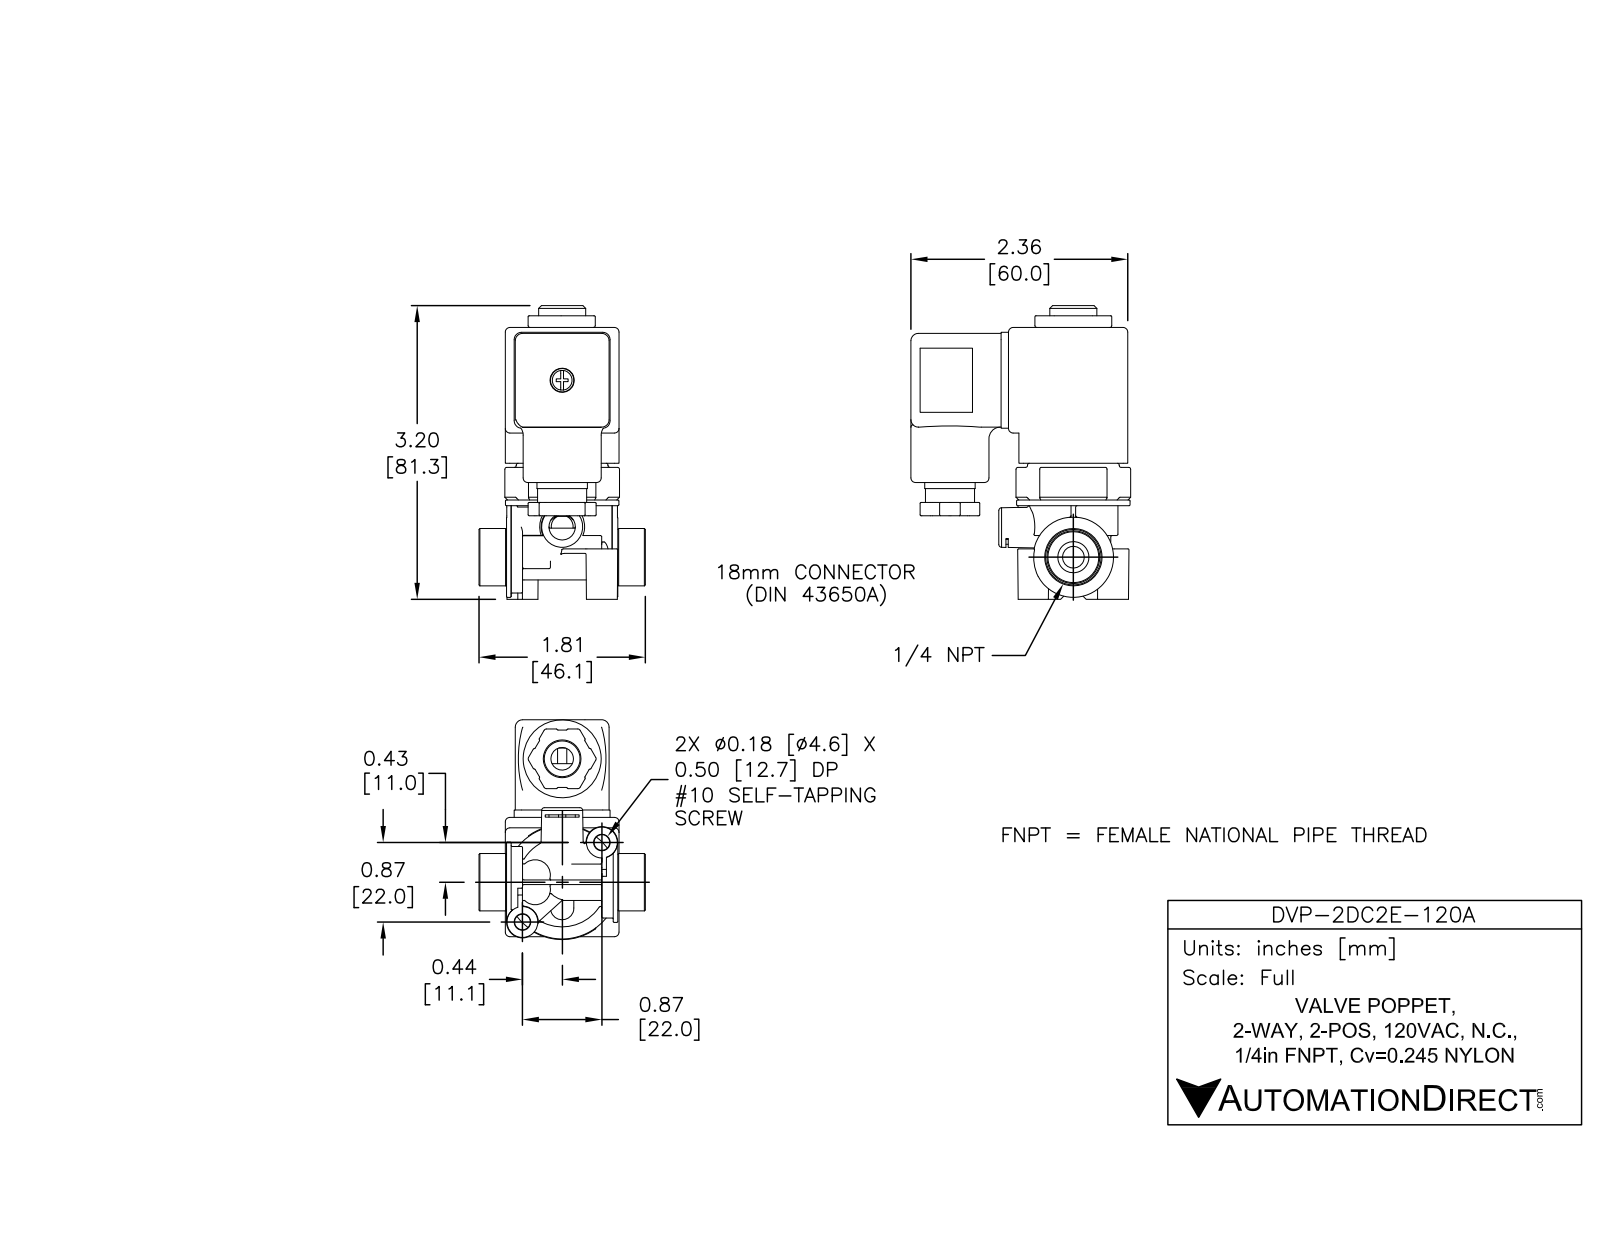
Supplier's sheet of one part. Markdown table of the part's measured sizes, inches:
| quantity | value |
| --- | --- |
| part name | DVP-2DC2E-120A |
| STEP written by | SolidWorks 2015 (AUTOMOTIVE_DESIGN) |
| units | inches |
| bodies | 6 solids, 1820 faces (805 planar, 354 cylindrical, 661 other) |
| overall size | 3.216 × 2.395 × 1.813 |
| volume | 3.952 in³ |
| surface area | 54.42 in² |
| round holes (diameter × count) | 0.06 × 2, 0.236 × 2, 0.095 × 1, 0.102 × 1, 0.12 × 1, 0.203 × 1, 0.245 × 1, 0.25 × 1, 0.263 × 1, 0.287 × 1, 0.37 × 1, 0.39 × 1 |
| round bosses / shafts (diameter × count) | 0.29 × 2, 1.236 × 1, 1 × 1, 0.972 × 1, 0.922 × 1, 0.89 × 1, 0.875 × 1, 0.85 × 1 |
| partial cylindrical surfaces (radius × count) | 0.01 × 75, 0.015 × 38, 0.05 × 21, 0.02 × 12, 0.08 × 12, 0.026 × 6, 0.03 × 6, 0.04 × 4 |
| main face-to-face distances | 1.083, 1.24, 0.048, 0.157, 0.925, 1.48, 0.109, 1.131, 0.974, 1.367 |
| hole center spacings | 0.281, 0.283, 1.062, 1.343, 1.345, 1.612, 1.626, 2.184 |
